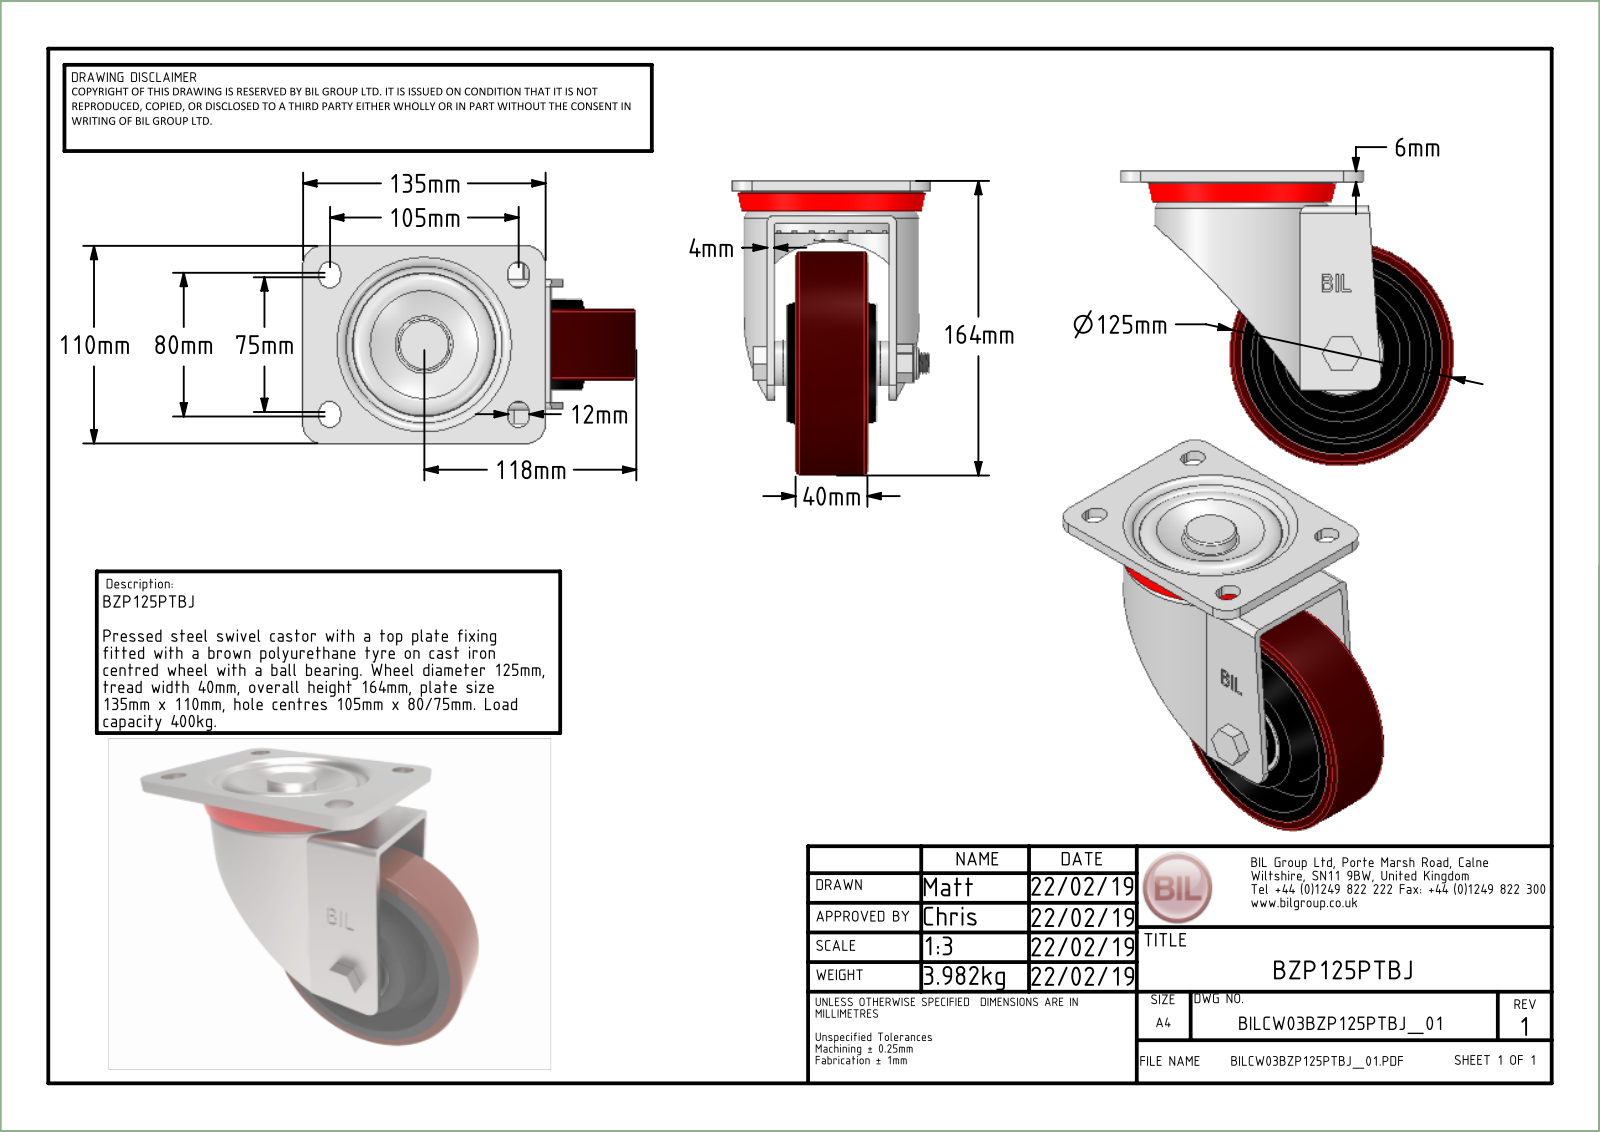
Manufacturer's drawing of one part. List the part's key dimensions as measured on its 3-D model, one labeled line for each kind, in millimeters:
Part name (STEP PRODUCT): BZP125PTBJ v3; BZP125AS - 64 v1; ZINC PLATED, PRESSED STEEL TOP PLATE; ZINC PLATED, PRESSED STEEL TOP PLATE Geometry (+8 more)
STEP written by: Autodesk Translation Framework v14.10.0.0 (AUTOMOTIVE_DESIGN)
Units: millimetres
Bodies: 40 solids, 1291 faces (615 planar, 241 cylindrical, 435 other)
Overall size (bounding box): 185.5 × 164 × 110
Volume: 630 546 mm³ · Surface area: 258 012 mm²
Round holes (diameter × count): ⌀12 ×1, ⌀12.2 ×1, ⌀12.5 ×1, ⌀12.75 ×1, ⌀14 ×1, ⌀19 ×1, ⌀20 ×1, ⌀28.5 ×1, ⌀30 ×1, ⌀30.8 ×1, ⌀40 ×1, ⌀40.3 ×1
Round bosses / shafts (diameter × count): ⌀105.5 ×1, ⌀96 ×1, ⌀83 ×1, ⌀50 ×1, ⌀40.8 ×1, ⌀31.3 ×1, ⌀29 ×1, ⌀27 ×1
Partial cylindrical surfaces — rounded edges, fillets, slot ends (radius × count): R0.5 ×20, R9.09 ×8, R0.47 ×4, R0.9 ×4, R2 ×4, R14 ×4, R0.89 ×2, R0.89 ×2
Main face-to-face distances: 16, 7, 4, 40, 36, 52, 12, 6, 68, 5
